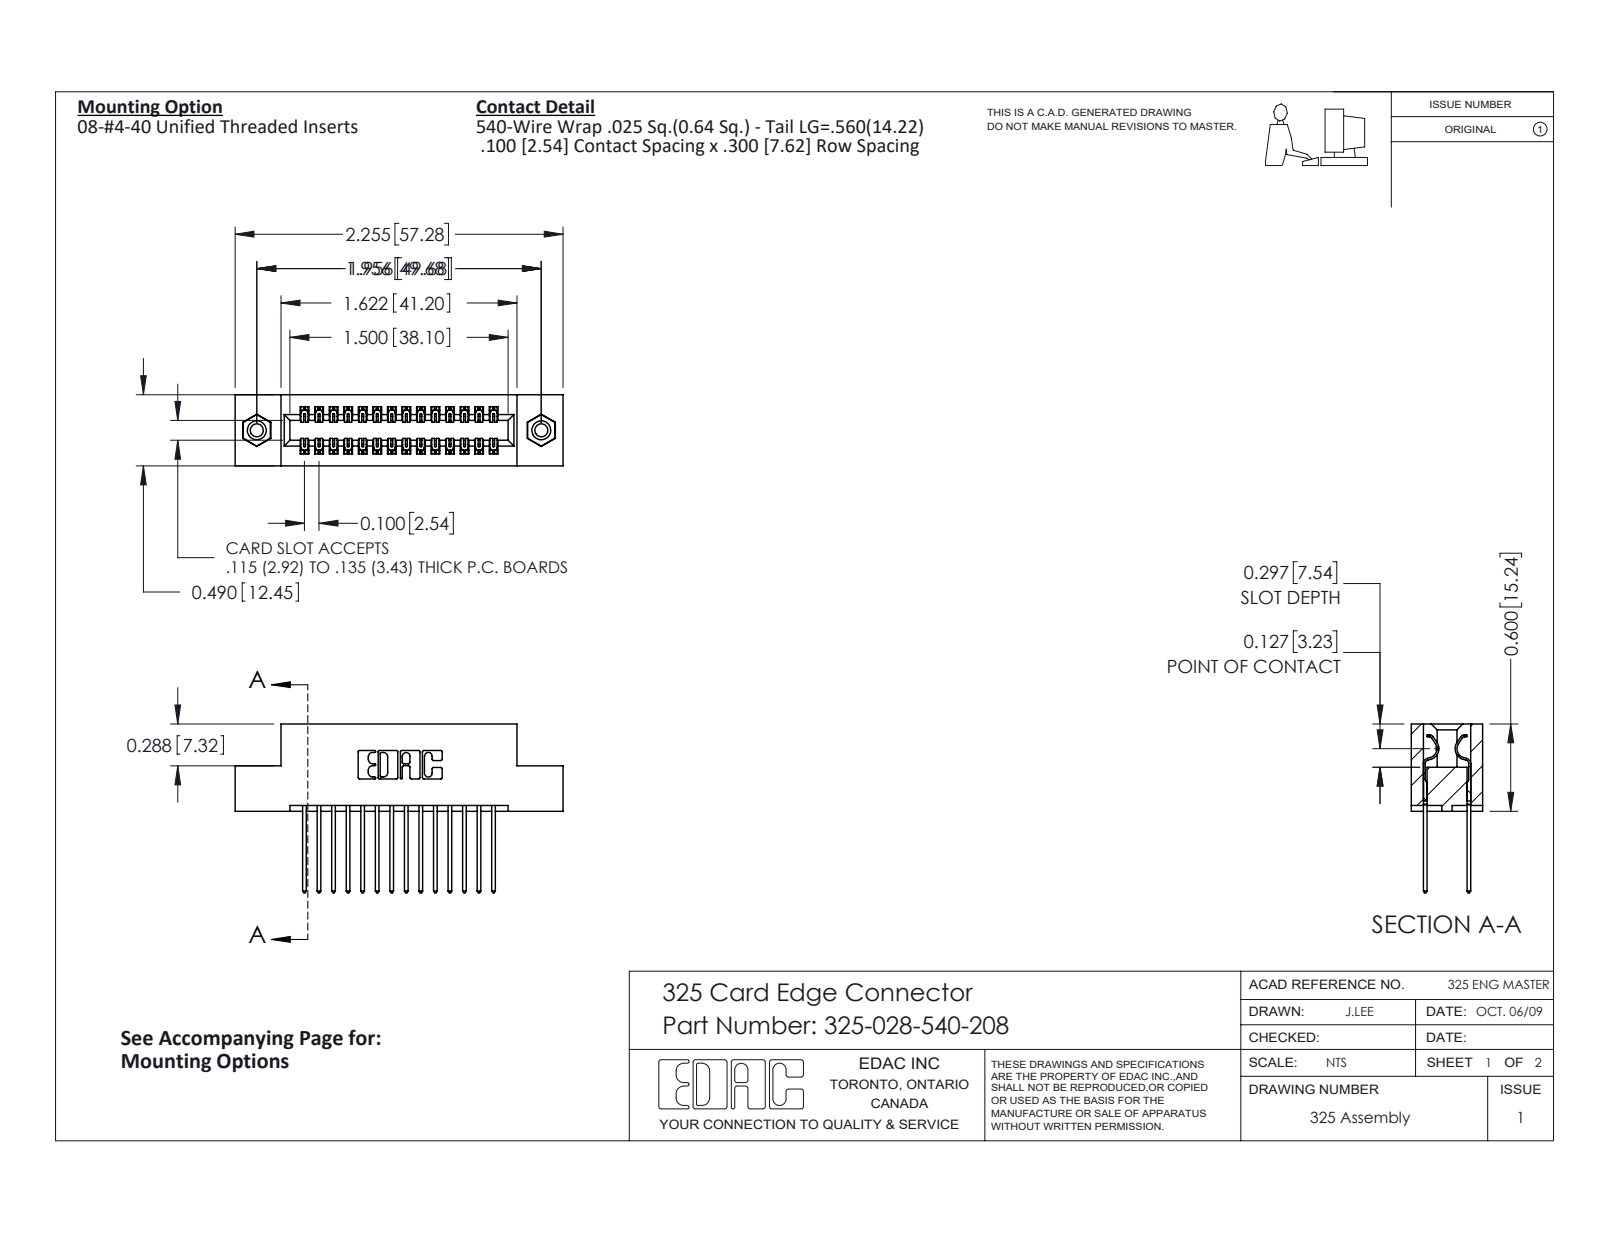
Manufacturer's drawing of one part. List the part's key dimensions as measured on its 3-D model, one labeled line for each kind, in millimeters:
Part name (STEP PRODUCT): 325 Part_TI; 325-028-540-208; 345-250-001_345-250-003-102; 325-292-001_325-293-140
STEP written by: SolidWorks 2016 (CONFIG_CONTROL_DESIGN)
Units: millimetres
Bodies: 31 solids, 1630 faces (1110 planar, 504 cylindrical, 16 other)
Overall size (bounding box): 57.3 × 29.5 × 12.4
Volume: 7 240 mm³ · Surface area: 8 619 mm²
Round holes (diameter × count): ⌀2.3 ×2, ⌀3.2 ×2, ⌀4.1 ×2
Round bosses / shafts (diameter × count): ⌀3.9 ×2
Partial cylindrical surfaces — rounded edges, fillets, slot ends (radius × count): R0.2 ×42, R0.3 ×28, R0.3 ×22, R0.2 ×6, R0.8 ×6, R0.7 ×3, R0.4 ×2, R0.6 ×2
Main face-to-face distances: 2.1, 10.3, 7.6, 2.7, 9.7, 0.6, 12.4, 8.3, 1, 2.5
Hole centre spacings: 49.7
